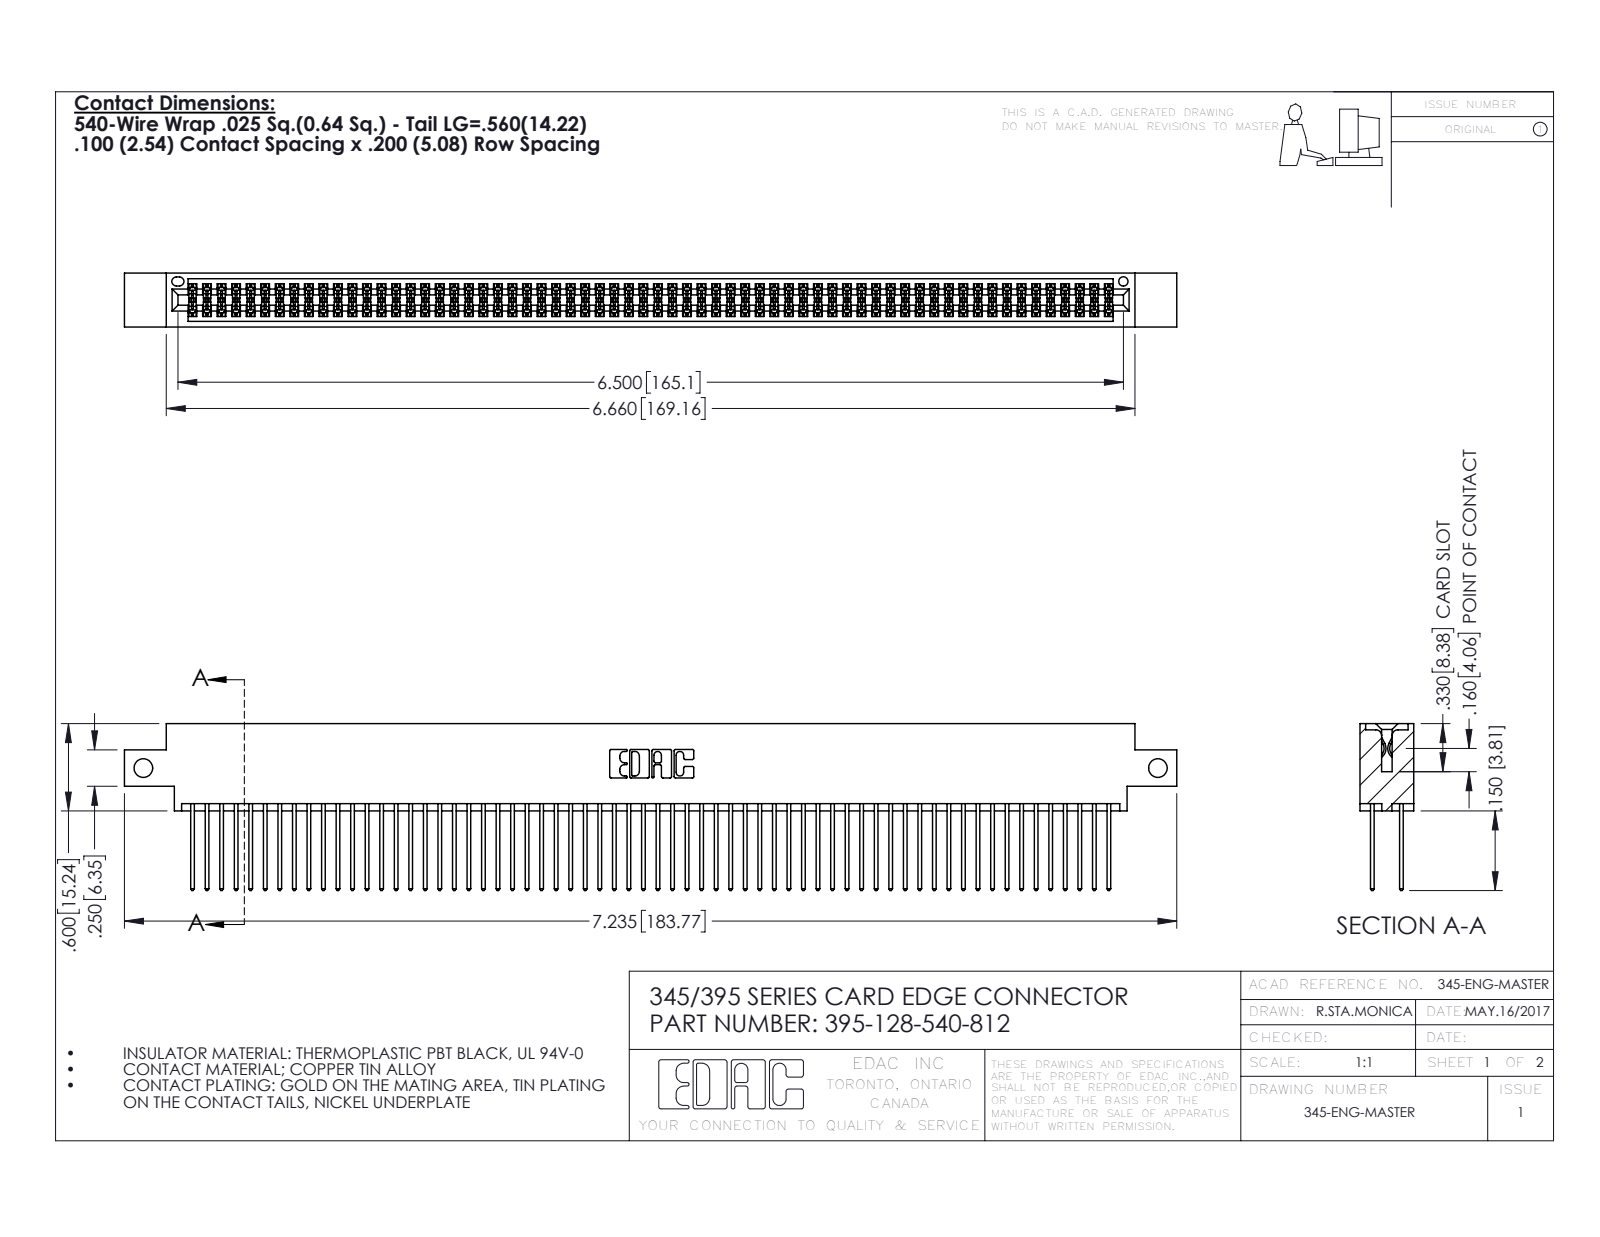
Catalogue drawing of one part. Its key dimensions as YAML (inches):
part_name: "395-128-540-812; 345 Part_0.170 Offset - Side Mount; 345-292-001_345-293-140"
step_written_by: "SolidWorks 2016 (CONFIG_CONTROL_DESIGN)"
units: inches
bodies: {solids: 129, faces: 6530, planar: 4308, cylindrical: 2222, other: 0}
overall_size: [7.235, 1.147, 0.37]
volume: 1.119
surface_area: 46.18
round_holes:
  - {diameter: 0.128, count: 2}
  - {diameter: 0.064, count: 1}
partial_cylinders:
  - {radius: 0.006, count: 192}
  - {radius: 0.01, count: 128}
  - {radius: 0.01, count: 22}
  - {radius: 0.007, count: 6}
  - {radius: 0.031, count: 6}
  - {radius: 0.026, count: 3}
  - {radius: 0.014, count: 2}
  - {radius: 0.019, count: 2}
face_to_face_distances: [0.072, 0.298, 0.2, 0.098, 0.272, 0.025, 0.37, 0.225, 0.175, 0.149]
hole_center_spacings: [6.975]
